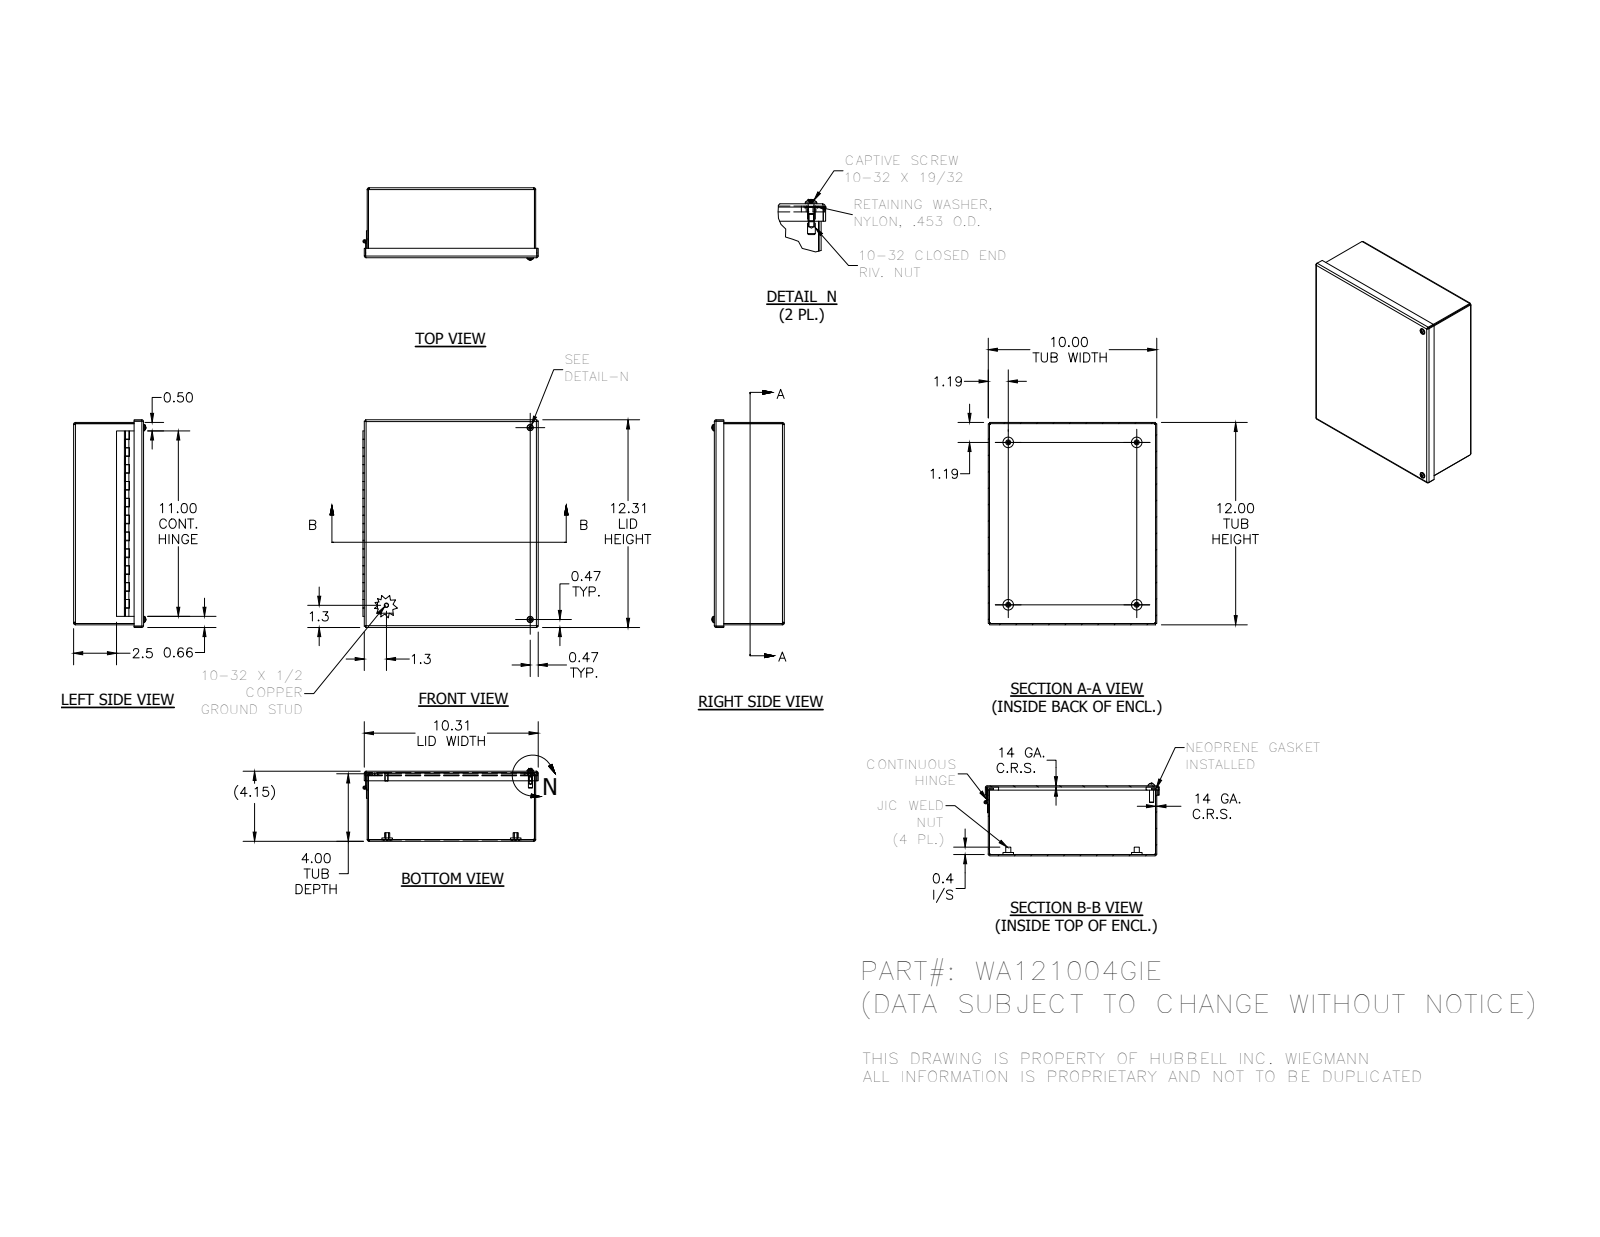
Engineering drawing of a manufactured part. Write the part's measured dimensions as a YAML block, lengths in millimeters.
part_name: "WA121004GIEBKP; 3499; 328123LH; 328123P (+8 more)"
step_written_by: "Autodesk Inventor 2014 (AUTOMOTIVE_DESIGN)"
units: millimeters
bodies: {solids: 18, faces: 485, planar: 281, cylindrical: 129, other: 75}
overall_size: [312.74, 264.08, 108.77]
volume: 656277
surface_area: 667905
round_holes:
  - {diameter: 3.96, count: 6}
  - {diameter: 6.53, count: 4}
  - {diameter: 7.94, count: 4}
  - {diameter: 4.98, count: 2}
  - {diameter: 7.06, count: 2}
  - {diameter: 7.14, count: 2}
  - {diameter: 2.96, count: 1}
round_bosses_or_shafts:
  - {diameter: 15.88, count: 4}
  - {diameter: 7.62, count: 4}
  - {diameter: 4.83, count: 3}
  - {diameter: 11.51, count: 2}
  - {diameter: 10.31, count: 2}
  - {diameter: 9.47, count: 2}
  - {diameter: 6.3, count: 2}
  - {diameter: 6.35, count: 1}
partial_cylinders:
  - {radius: 0.79, count: 12}
  - {radius: 2.67, count: 12}
  - {radius: 1.78, count: 8}
  - {radius: 2.27, count: 2}
face_to_face_distances: [1.88, 103.58, 101.7, 105.46, 252.12, 302.92, 254, 250.24, 304.8, 301.04]
hole_center_spacings: [288.92, 31.42, 217.04, 238.12, 288.91, 238.41, 267.62, 343.14]
